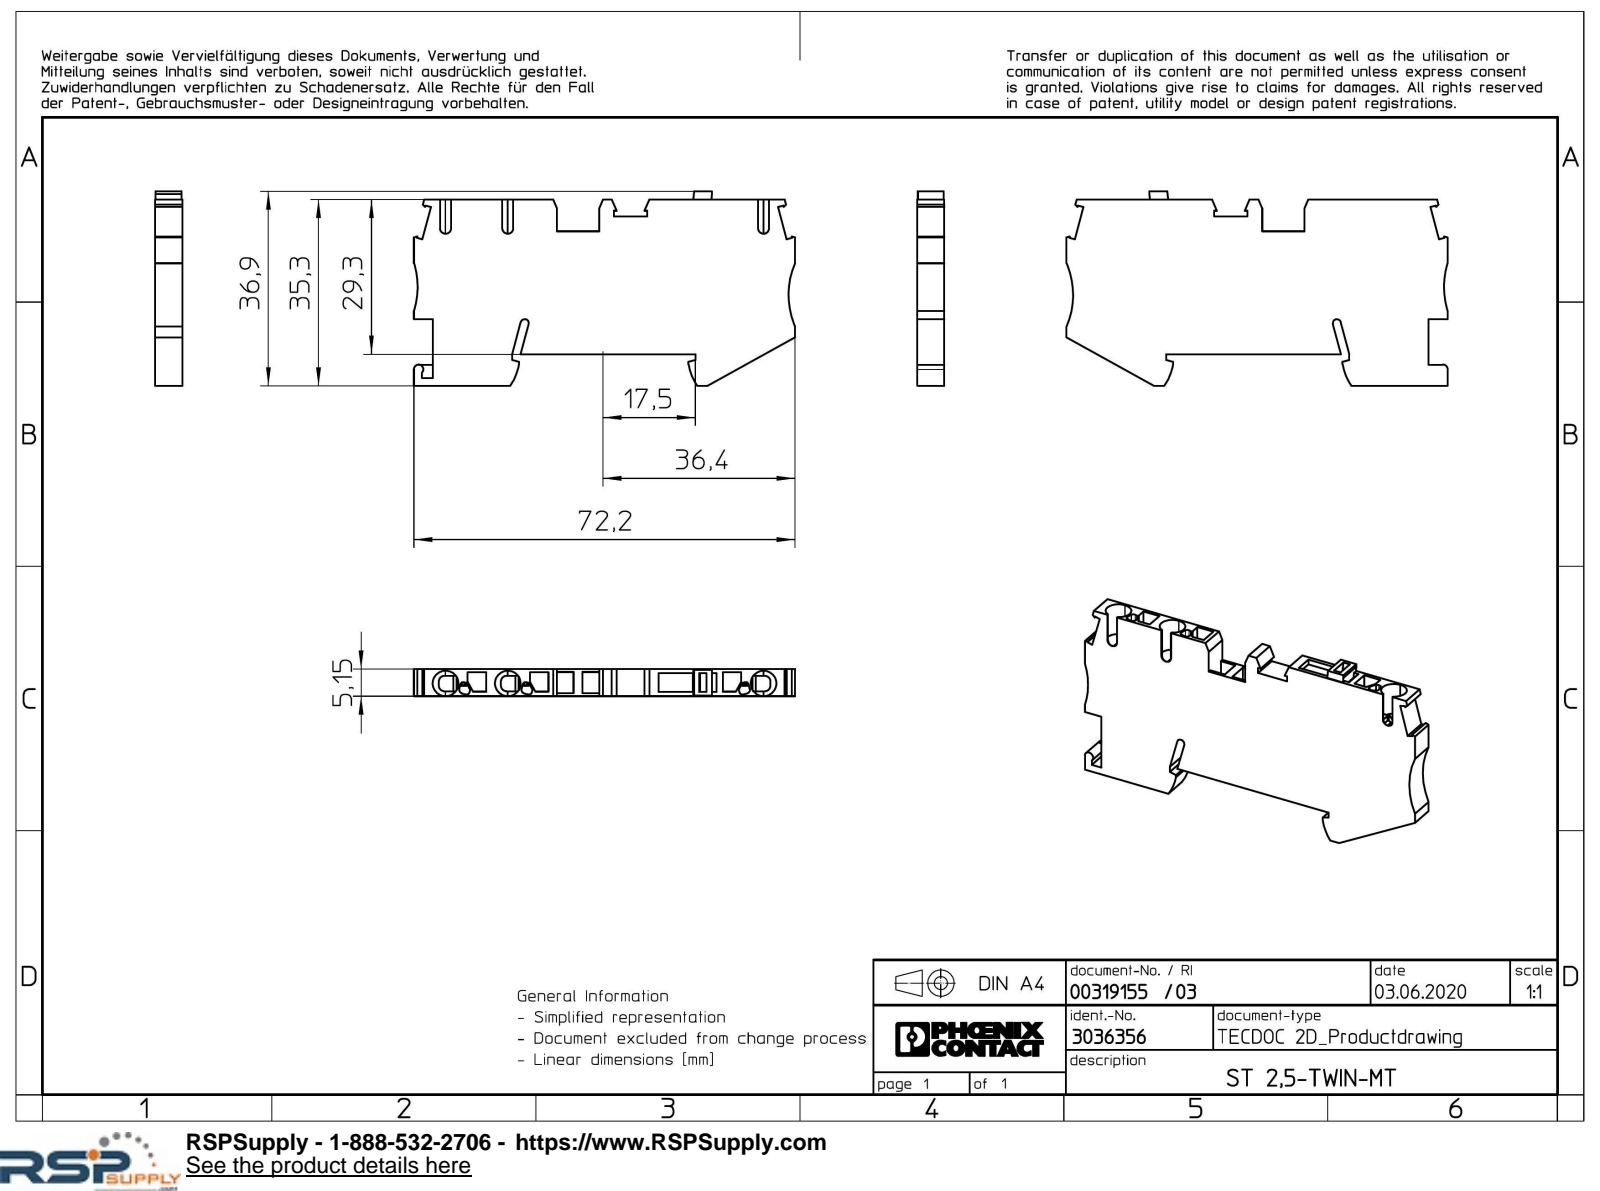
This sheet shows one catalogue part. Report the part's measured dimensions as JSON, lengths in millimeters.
{"part_name": "st25_twin_mt_select", "step_written_by": "Creo Elements/Direct Modeling 20.1A 29-Sep-2018 (C) Parametric Technology GmbH (AUTOMOTIVE_DESIGN)", "units": "millimeters", "bodies": {"solids": 1, "faces": 233, "planar": 180, "cylindrical": 38, "other": 15}, "overall_size": [72.2, 36.85, 5.15], "volume_mm3": 9524, "surface_area_mm2": 7104, "partial_cylinders_radius": [[1, 12], [2.4, 6], [0.5, 3], [0.6, 3], [0.67, 3], [9.5, 2], [15, 2], [0.2, 1]], "face_to_face_distances": [5.15, 29.25, 0.65, 6, 35.25, 3.15, 4.85, 4.5, 4, 0.58]}
